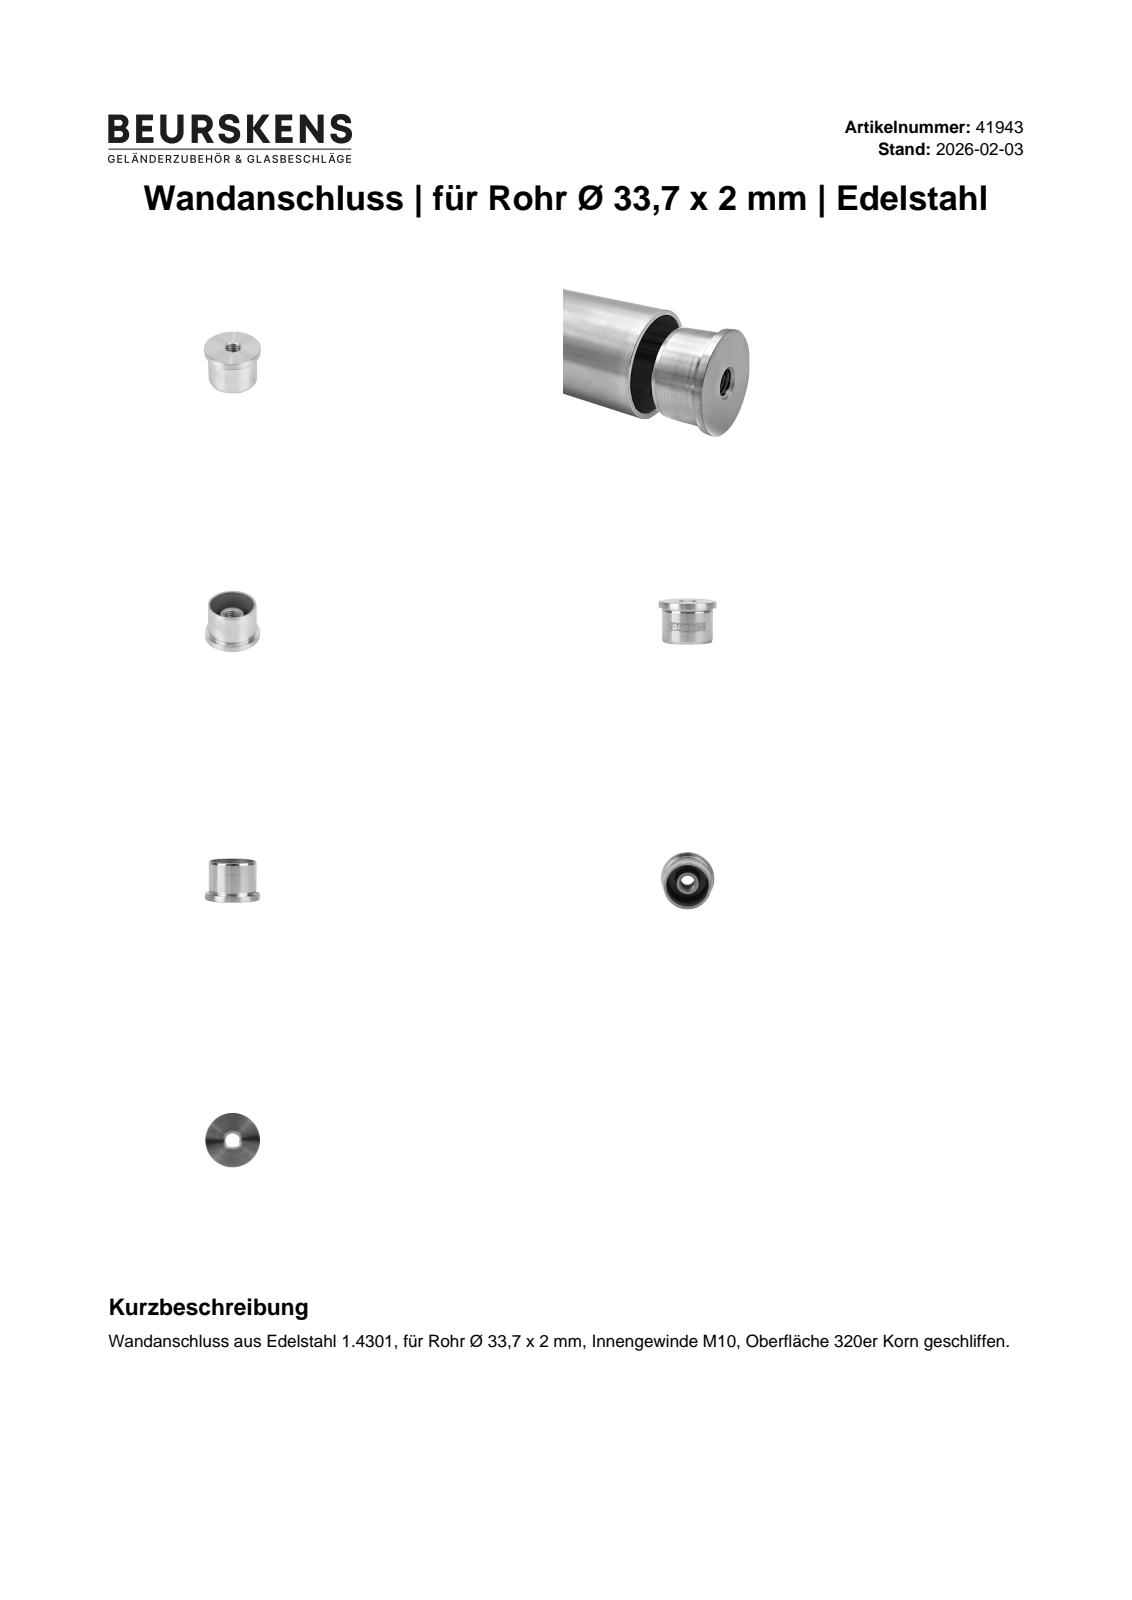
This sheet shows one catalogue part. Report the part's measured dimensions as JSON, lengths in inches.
{"part_name": "41943", "step_written_by": "Autodesk Inventor 2022 (AUTOMOTIVE_DESIGN)", "units": "inches", "bodies": {"solids": 1, "faces": 10, "planar": 4, "cylindrical": 5, "other": 1}, "overall_size": [1.327, 1.327, 0.925], "volume_in3": 0.434, "surface_area_in2": 11.11, "round_holes": [[0.394, 1], [1.012, 1]], "round_bosses_or_shafts": [[1.327, 1], [1.169, 1], [0.551, 1]], "face_to_face_distances": [0.079, 0.059, 0.138, 0.787, 0.846, 0.925]}
